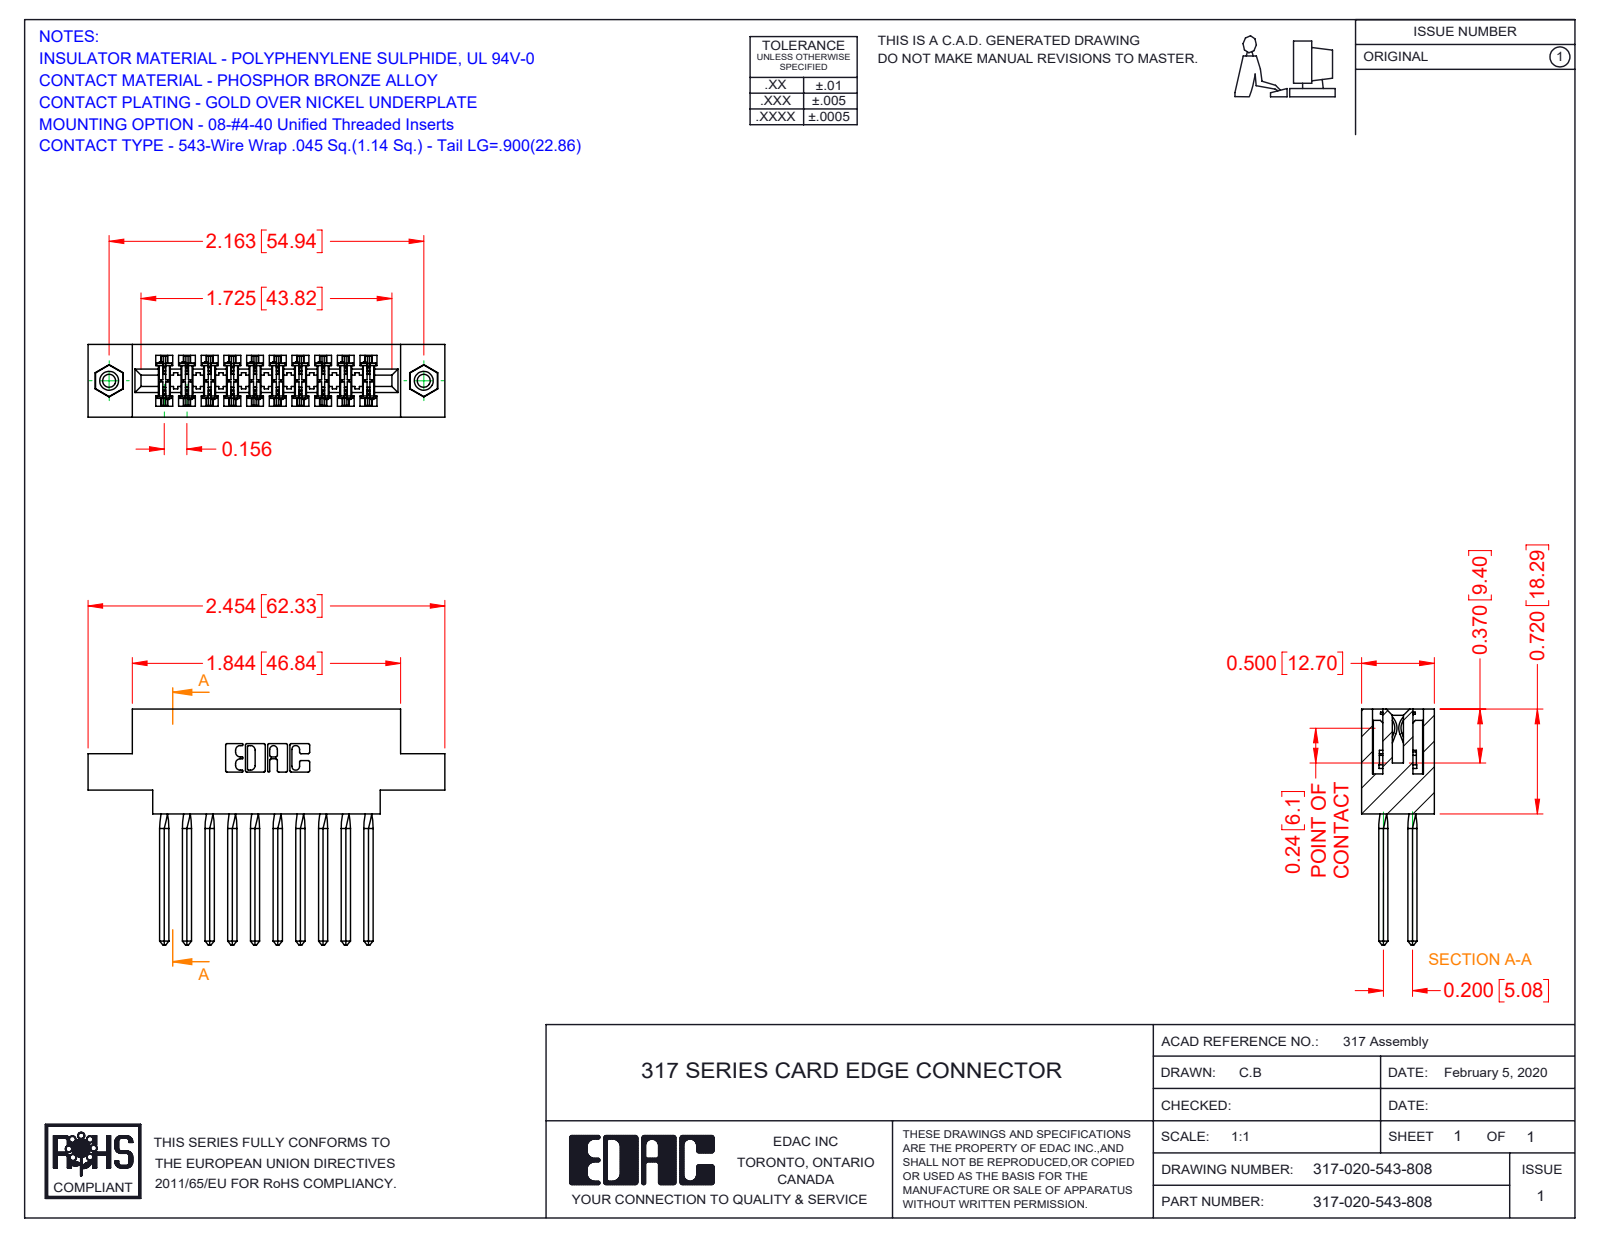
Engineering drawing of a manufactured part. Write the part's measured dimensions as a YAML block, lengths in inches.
part_name: "317-020-543-878; 317-290-001_543; 317 Part_.156 Dia - TI; 345-250-001_345-250-003-102"
step_written_by: "SolidWorks 2016 (CONFIG_CONTROL_DESIGN)"
units: inches
bodies: {solids: 23, faces: 1942, planar: 1550, cylindrical: 296, other: 96}
overall_size: [2.454, 1.62, 0.5]
volume: 0.578
surface_area: 20.36
round_holes:
  - {diameter: 0.089, count: 2}
  - {diameter: 0.125, count: 2}
  - {diameter: 0.156, count: 2}
round_bosses_or_shafts:
  - {diameter: 0.155, count: 2}
partial_cylinders:
  - {radius: 0.015, count: 40}
  - {radius: 0.01, count: 22}
  - {radius: 0.007, count: 6}
  - {radius: 0.031, count: 6}
  - {radius: 0.026, count: 3}
  - {radius: 0.095, count: 2}
  - {radius: 0.1, count: 2}
  - {radius: 0.11, count: 2}
face_to_face_distances: [0.5, 0.11, 0.075, 0.425, 0.22, 0.331, 0.35, 0.156, 0.116, 0.441]
hole_center_spacings: [2.163]
